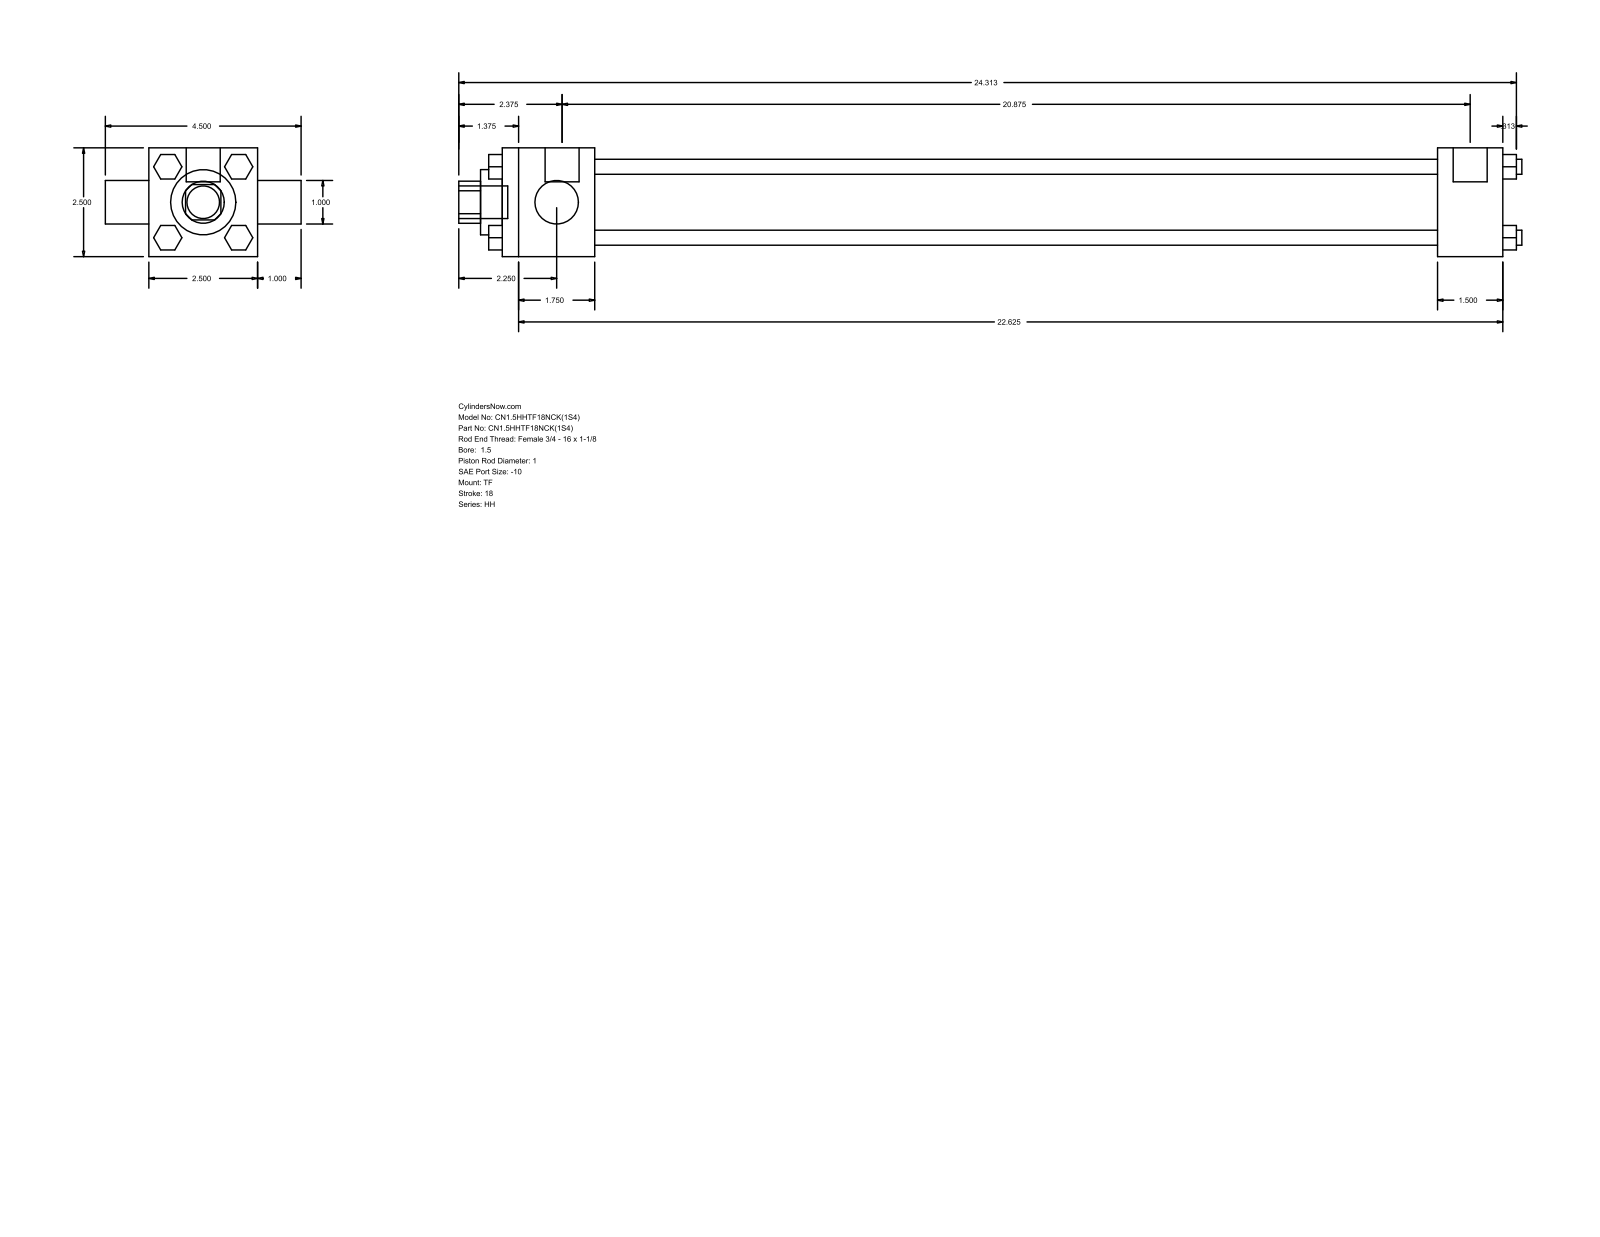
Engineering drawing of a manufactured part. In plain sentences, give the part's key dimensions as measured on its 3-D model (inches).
The part is named "HH_TF__0150_1". Its 3-D file was written by "GSSL Pune (CONFIG_CONTROL_DESIGN)". It is 0 solids with 120 faces: 92 planar, 28 cylindrical and 0 other. Overall it measures 24.437 by 4.5 by 2.5 inches. Round holes: 2 of diameter 1, 1 of diameter 1.5, 1 of diameter 1.75. Round bosses or shafts: 4 of diameter 0.345, 3 of diameter 0.219, 2 of diameter 0.781, 1 of diameter 0.75. Partial cylindrical surfaces (rounded edges, fillets, slot ends): 1 of radius 0.484. The main face-to-face distances are 2.5, 20.875, 19.375, 1.5, 2.125, 21.5, 23, 23.313, 1, 0.815.
